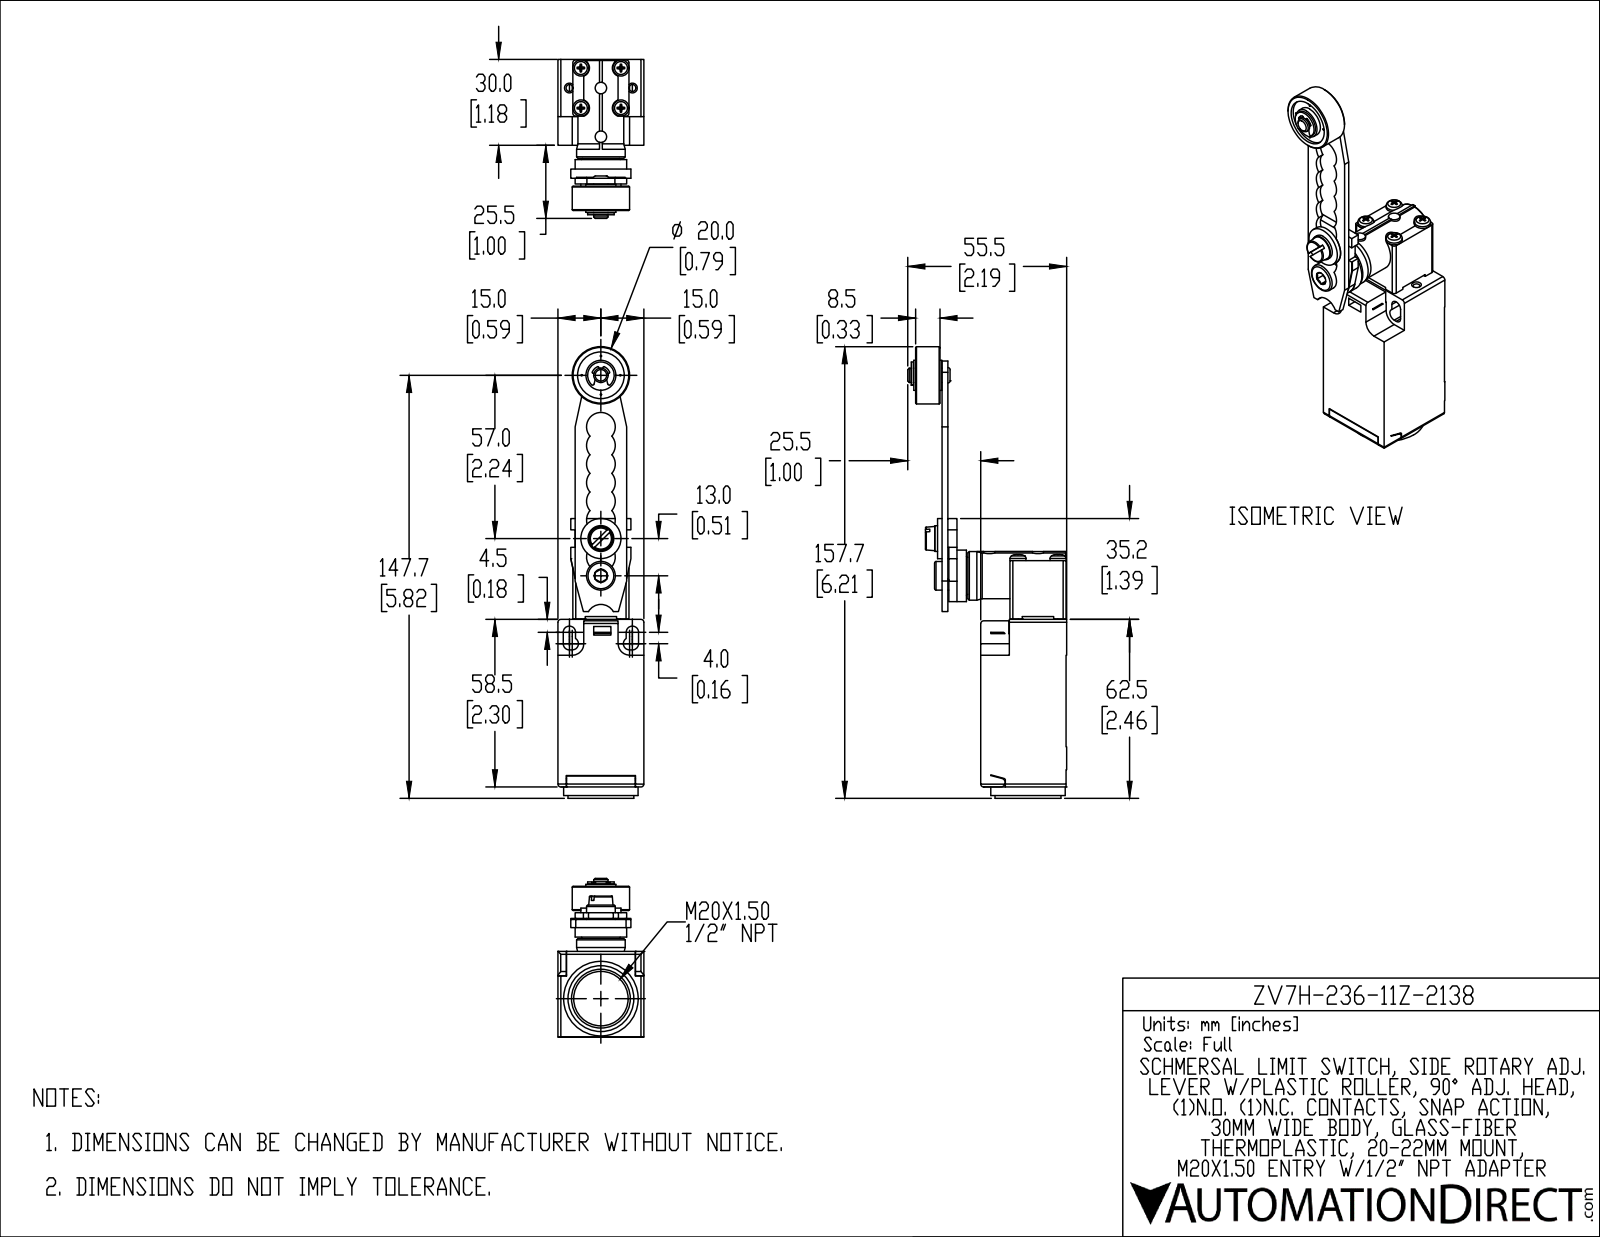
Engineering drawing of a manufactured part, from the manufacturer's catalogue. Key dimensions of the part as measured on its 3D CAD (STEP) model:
Part name (STEP PRODUCT): ZV7H-236-11Z-2138
STEP written by: SolidWorks 2019 (AUTOMOTIVE_DESIGN)
Units: inches
Bodies: 6 solids, 457 faces (303 planar, 120 cylindrical, 34 other)
Overall size (bounding box): 6.209 × 2.185 × 1.181
Volume: 4.049 in³ · Surface area: 32.22 in²
Round holes (diameter × count): ⌀0.094 ×6, ⌀0.02 ×4, ⌀0.126 ×4, ⌀0.512 ×1, ⌀0.545 ×1, ⌀0.551 ×1, ⌀0.642 ×1, ⌀0.748 ×1
Round bosses / shafts (diameter × count): ⌀0.221 ×4, ⌀0.213 ×4, ⌀0.157 ×3, ⌀1.024 ×1, ⌀0.906 ×1, ⌀0.787 ×1, ⌀0.709 ×1, ⌀0.669 ×1
Partial cylindrical surfaces — rounded edges, fillets, slot ends (radius × count): R0.197 ×11, R0.039 ×10, R0.085 ×6, R0.059 ×5, R0.012 ×4, R0.118 ×4, R0.02 ×2, R0.157 ×2
Main face-to-face distances: 1.181, 1.173, 0.205, 0.079, 0.531, 1.705, 0.453, 1.626, 0.976, 0.236
Hole centre spacings: 0.266, 0.317, 0.376, 0.39, 0.551, 0.76, 0.308, 0.433
